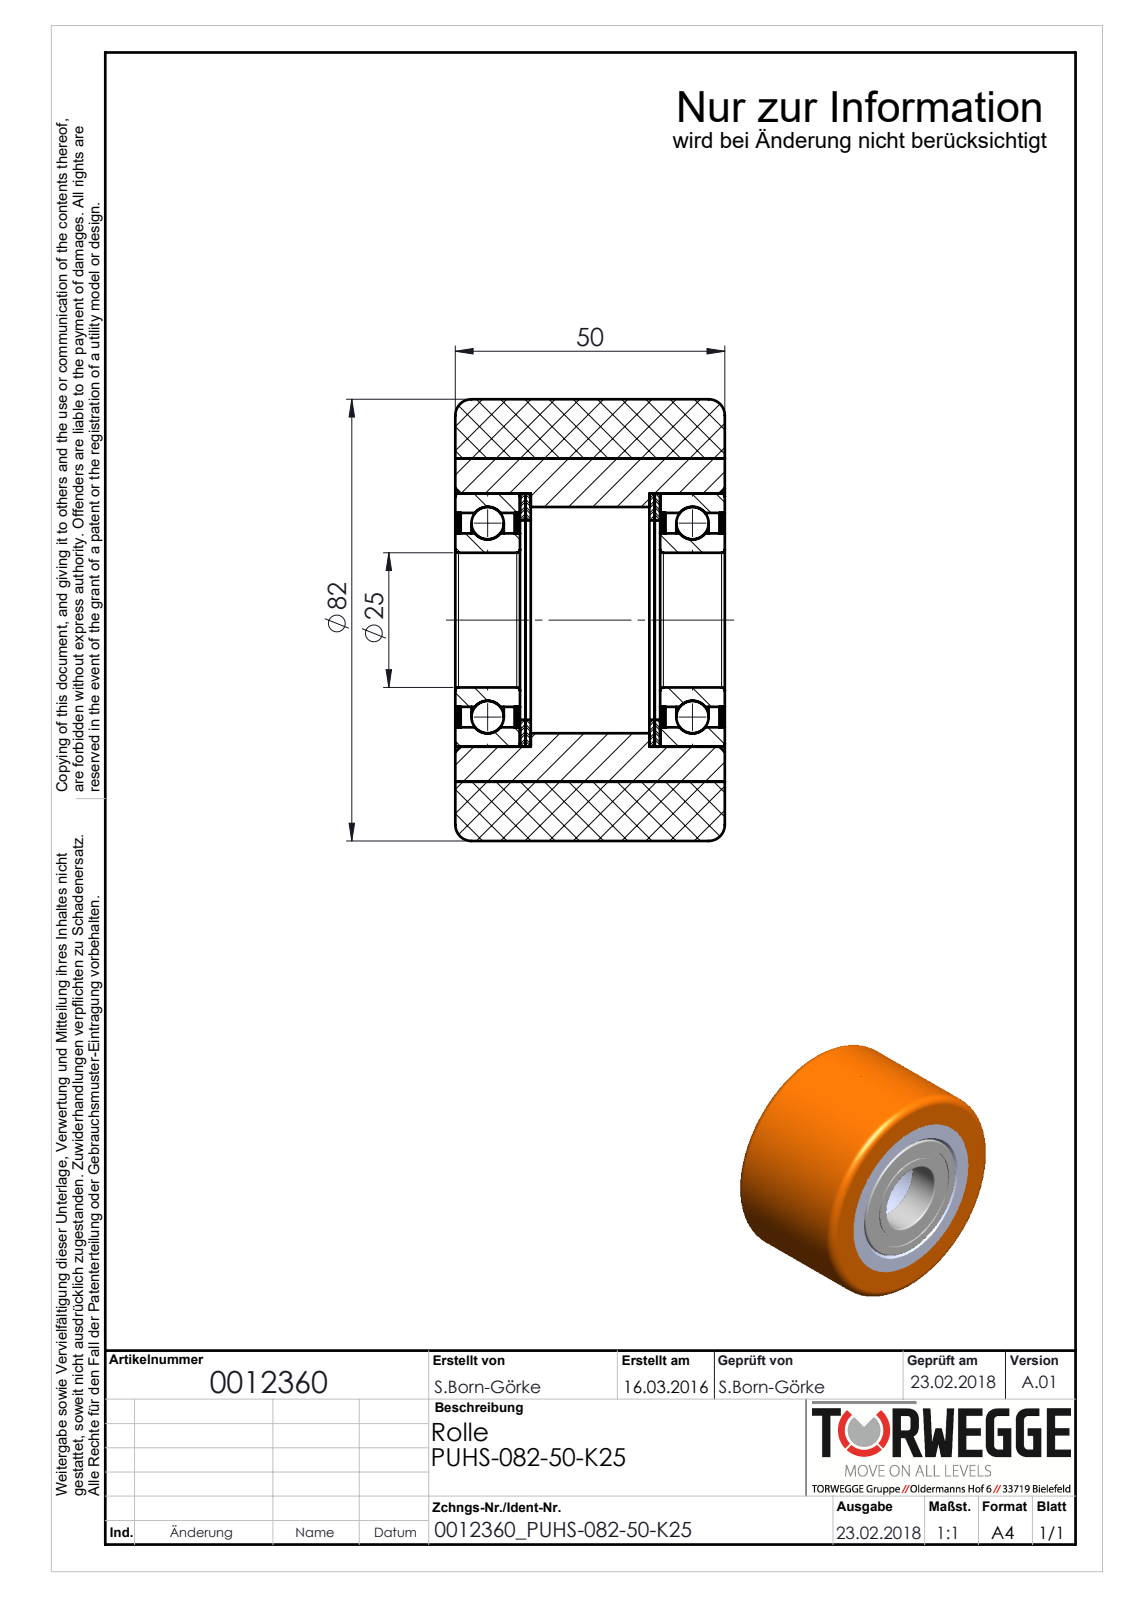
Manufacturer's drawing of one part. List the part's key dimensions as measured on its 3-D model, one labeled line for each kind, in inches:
Part name (STEP PRODUCT): 0012360_PUHS-082-50-K25
STEP written by: SolidWorks 2016 (AUTOMOTIVE_DESIGN)
Units: inches
Bodies: 16 solids, 158 faces (30 planar, 68 cylindrical, 60 other)
Overall size (bounding box): 3.228 × 3.228 × 1.969
Volume: 12.9 in³ · Surface area: 115.1 in²
Round holes (diameter × count): ⌀0.984 ×1, ⌀1.268 ×1, ⌀1.457 ×1, ⌀1.567 ×1, ⌀1.654 ×1, ⌀2.362 ×1
Round bosses / shafts (diameter × count): ⌀3.228 ×1, ⌀1.85 ×1
Main face-to-face distances: 0.039, 1.496, 0.472, 0.02, 0.512, 1.457, 0.984, 1.969, 0.945, 1.417
